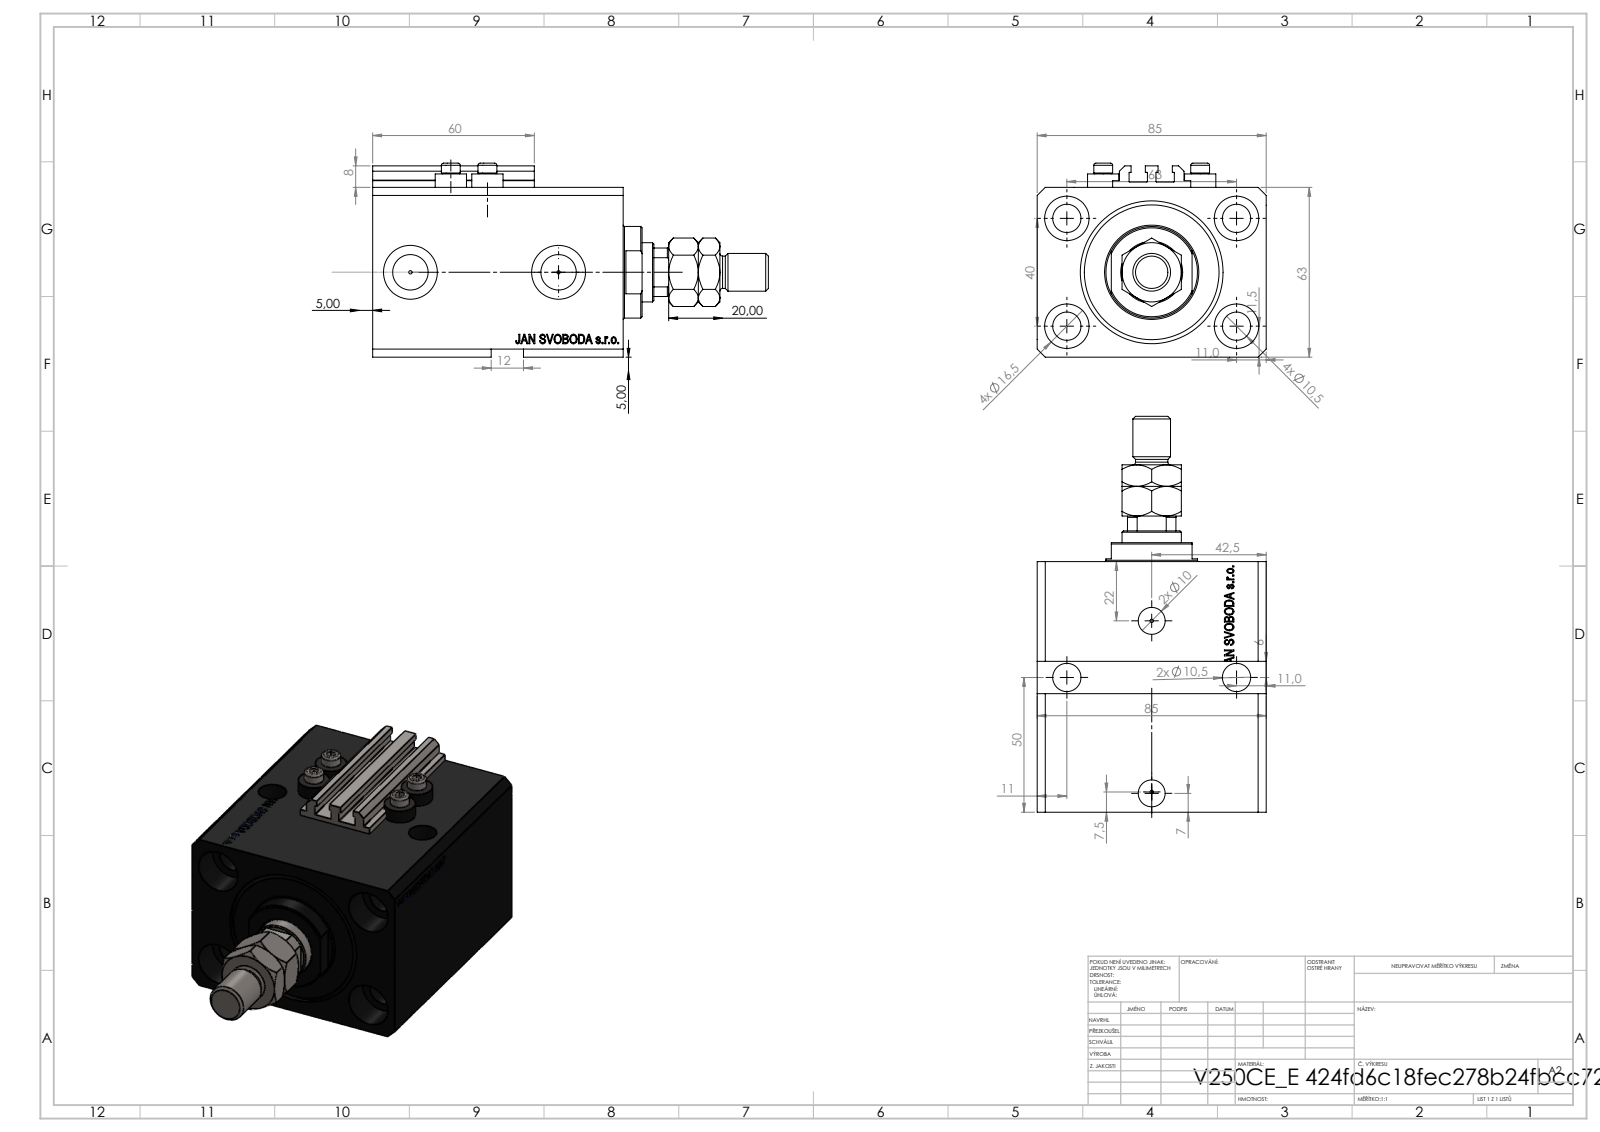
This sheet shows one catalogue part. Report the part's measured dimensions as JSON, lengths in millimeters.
{"part_name": "V250CE_E_Body; V250CE_C_VCP; ALLEN BOLT V250CE; V250CE_VC_E (+1 more)", "step_written_by": "SolidWorks 2019 (CONFIG_CONTROL_DESIGN)", "units": "millimeters", "bodies": {"solids": 9, "faces": 1136, "planar": 550, "cylindrical": 130, "other": 456}, "overall_size": [146.9, 85, 72], "volume_mm3": 447770, "surface_area_mm2": 100992, "round_holes": [[10.5, 6], [1.25, 4], [4, 4], [16.5, 4], [10, 2], [13.16, 2], [20, 2], [12.5, 1], [22, 1], [40, 1], [53, 1]], "round_bosses_or_shafts": [[11.6, 4], [7, 4], [34, 1], [14, 1], [12, 1]], "partial_cylinders_radius": [[0.2, 10], [10.5, 1]], "face_to_face_distances": [63, 85, 93, 65.9, 54.5, 27.1, 11.4, 81.6, 3, 65], "hole_center_spacings": [37.31, 63, 13.6, 15.4, 24.96, 28.02, 28.43, 33.62]}
